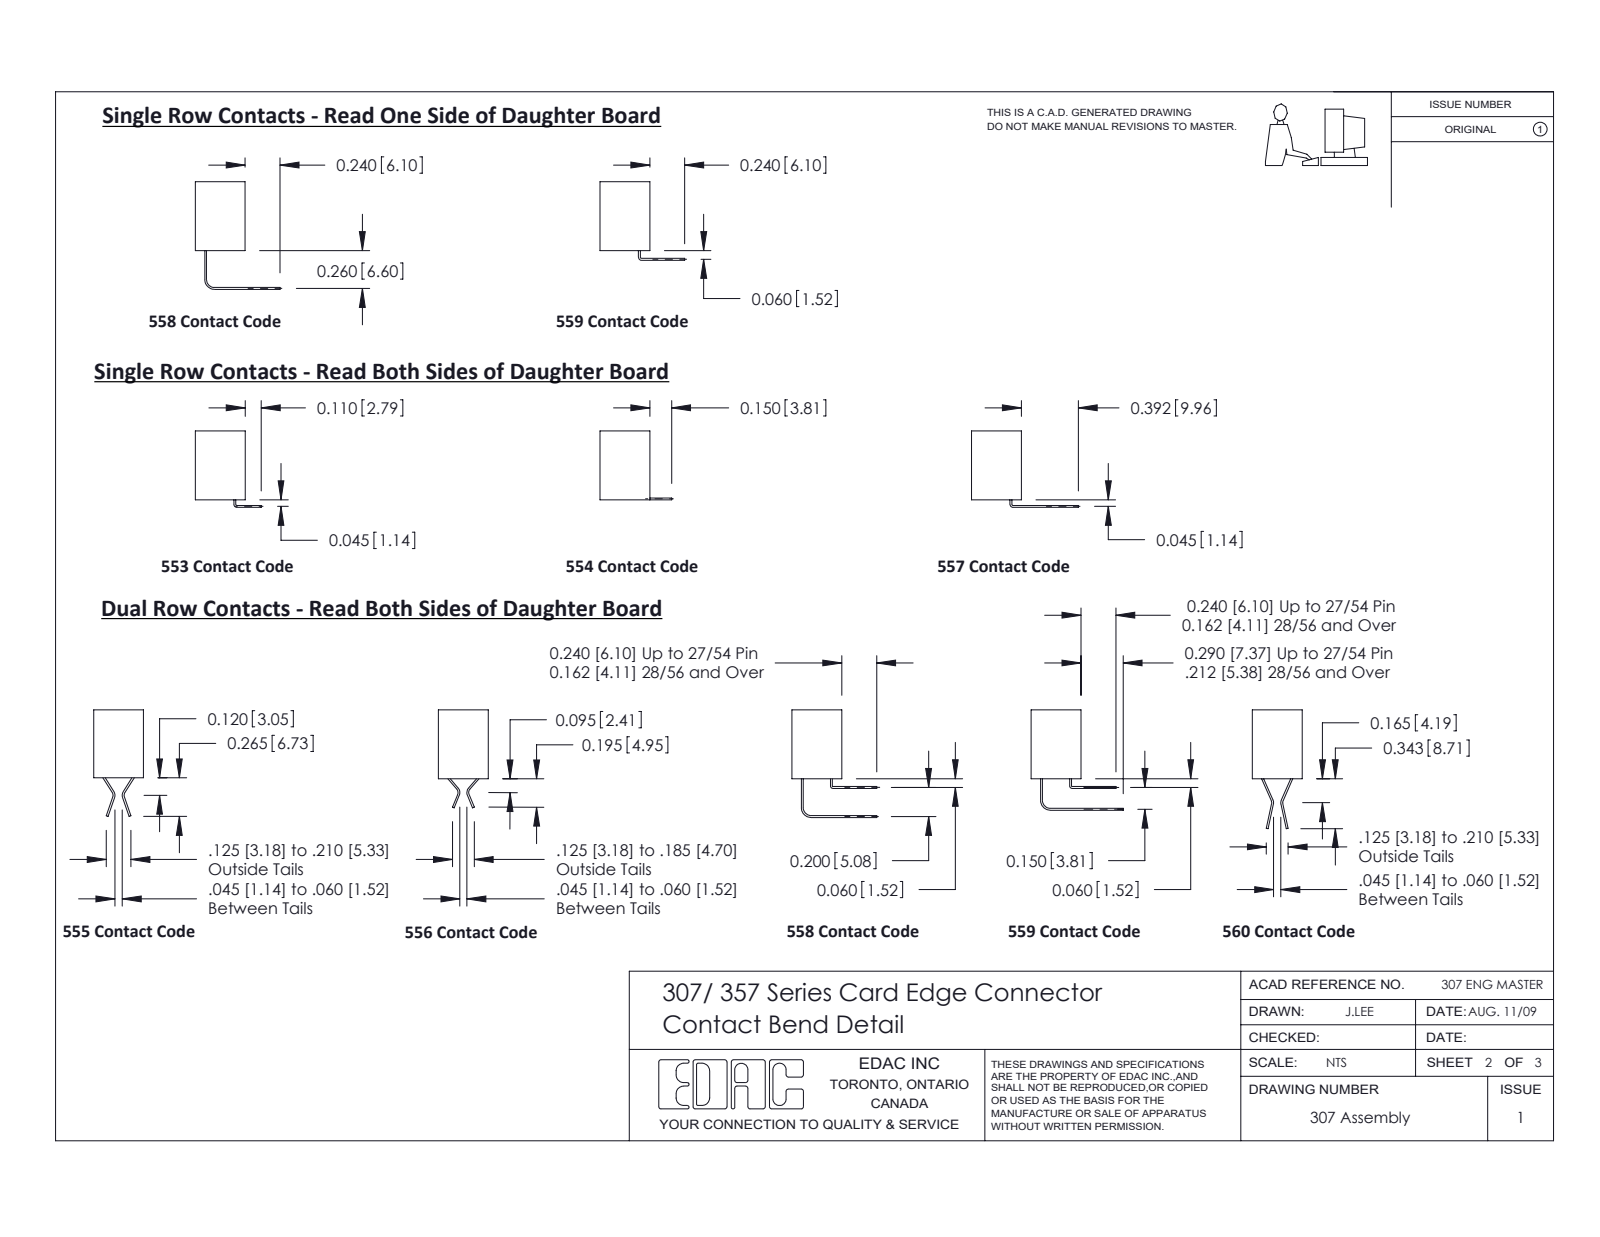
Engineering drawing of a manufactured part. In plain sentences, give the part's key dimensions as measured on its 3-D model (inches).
The part is named "357-007-421-104; 307 Part_.156 Dia Mounting Holes; 307-290-002_521". Its 3-D file was written by "SolidWorks 2020 (CONFIG_CONTROL_DESIGN)". It is 8 solids with 658 faces: 399 planar, 243 cylindrical and 16 other. Overall it measures 1.998 by 0.686 by 0.343 inches. Its volume is 0.198 cubic inches and its surface area 7.67 square inches. Round holes: 2 of diameter 0.156. Partial cylindrical surfaces (rounded edges, fillets, slot ends): 26 of radius 0.02, 22 of radius 0.01, 7 of radius 0.023, 6 of radius 0.007, 6 of radius 0.031, 3 of radius 0.026, 2 of radius 0.012, 2 of radius 0.025. The main face-to-face distances are 0.013, 0.064, 0.343, 0.279, 0.156, 0.202, 0.279, 0.215, 0.064, 0.077. The hole center spacings are 1.688.
